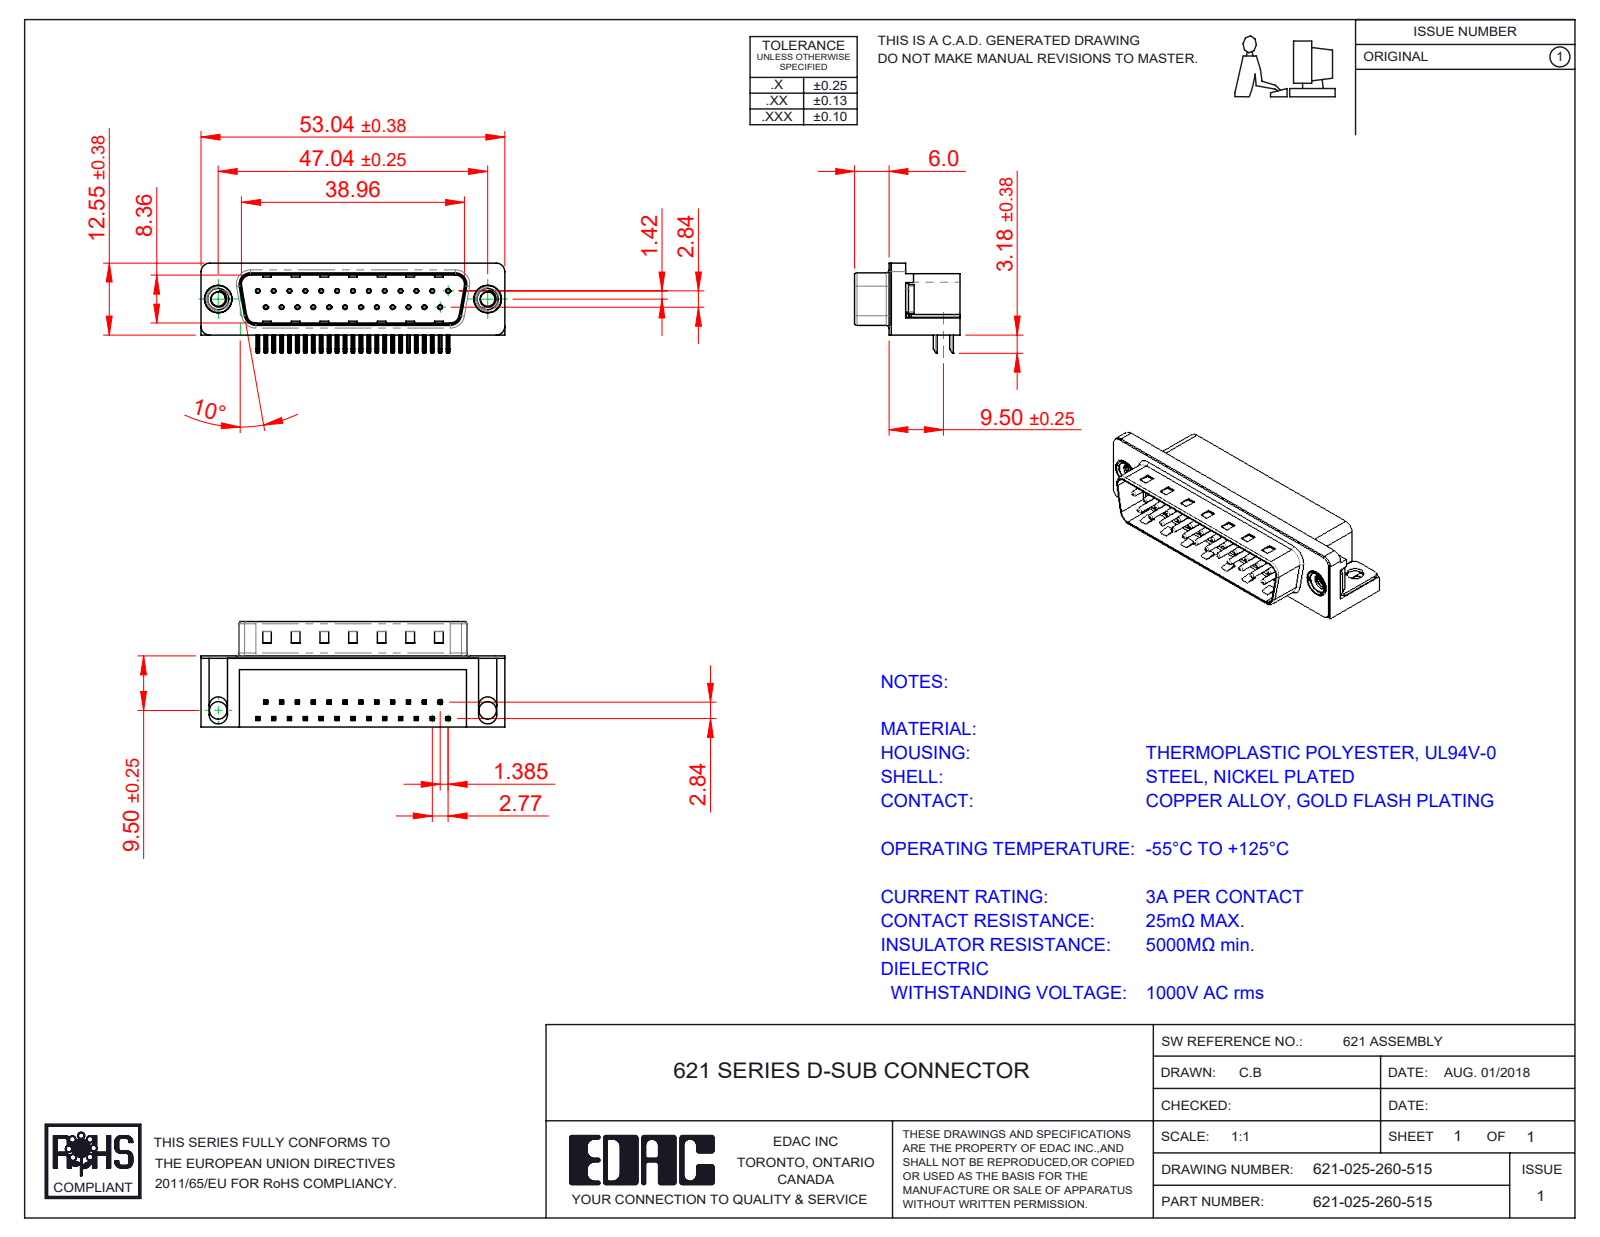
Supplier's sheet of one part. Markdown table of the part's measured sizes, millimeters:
| quantity | value |
| --- | --- |
| part name | 621 Contact Bottom; 621 M3 Threaded Rivet; 621 Housing_25 Socket; 621 Thru Hole Board Mount (+3 more) |
| STEP written by | SolidWorks 2016 (CONFIG_CONTROL_DESIGN) |
| units | millimeters |
| bodies | 31 solids, 2261 faces (1403 planar, 663 cylindrical, 195 other) |
| overall size | 53.04 × 18.4 × 15.73 |
| volume | 6 340 mm³ |
| surface area | 7 673 mm² |
| round holes (diameter × count) | 0.35 × 25, 0.8 × 25, 2.5 × 2, 3.05 × 2, 4 × 2, 4.8 × 2, 5 × 2 |
| round bosses / shafts (diameter × count) | 0.75 × 25, 4.9 × 2, 4.75 × 2, 3.9 × 2 |
| partial cylindrical surfaces (radius × count) | 0.25 × 108, 0.12 × 50, 1 × 16, 0.5 × 9, 1.6 × 8, 1.5 × 7, 0.9 × 4, 2 × 4 |
| main face-to-face distances | 0.4, 12, 10.35, 2.1, 8.76, 10.46, 1.7, 10.86, 12.4, 9 |
| hole center spacings | 3.16, 2.77, 5.54, 8.31, 11.08, 13.85, 16.62, 5.03 |
